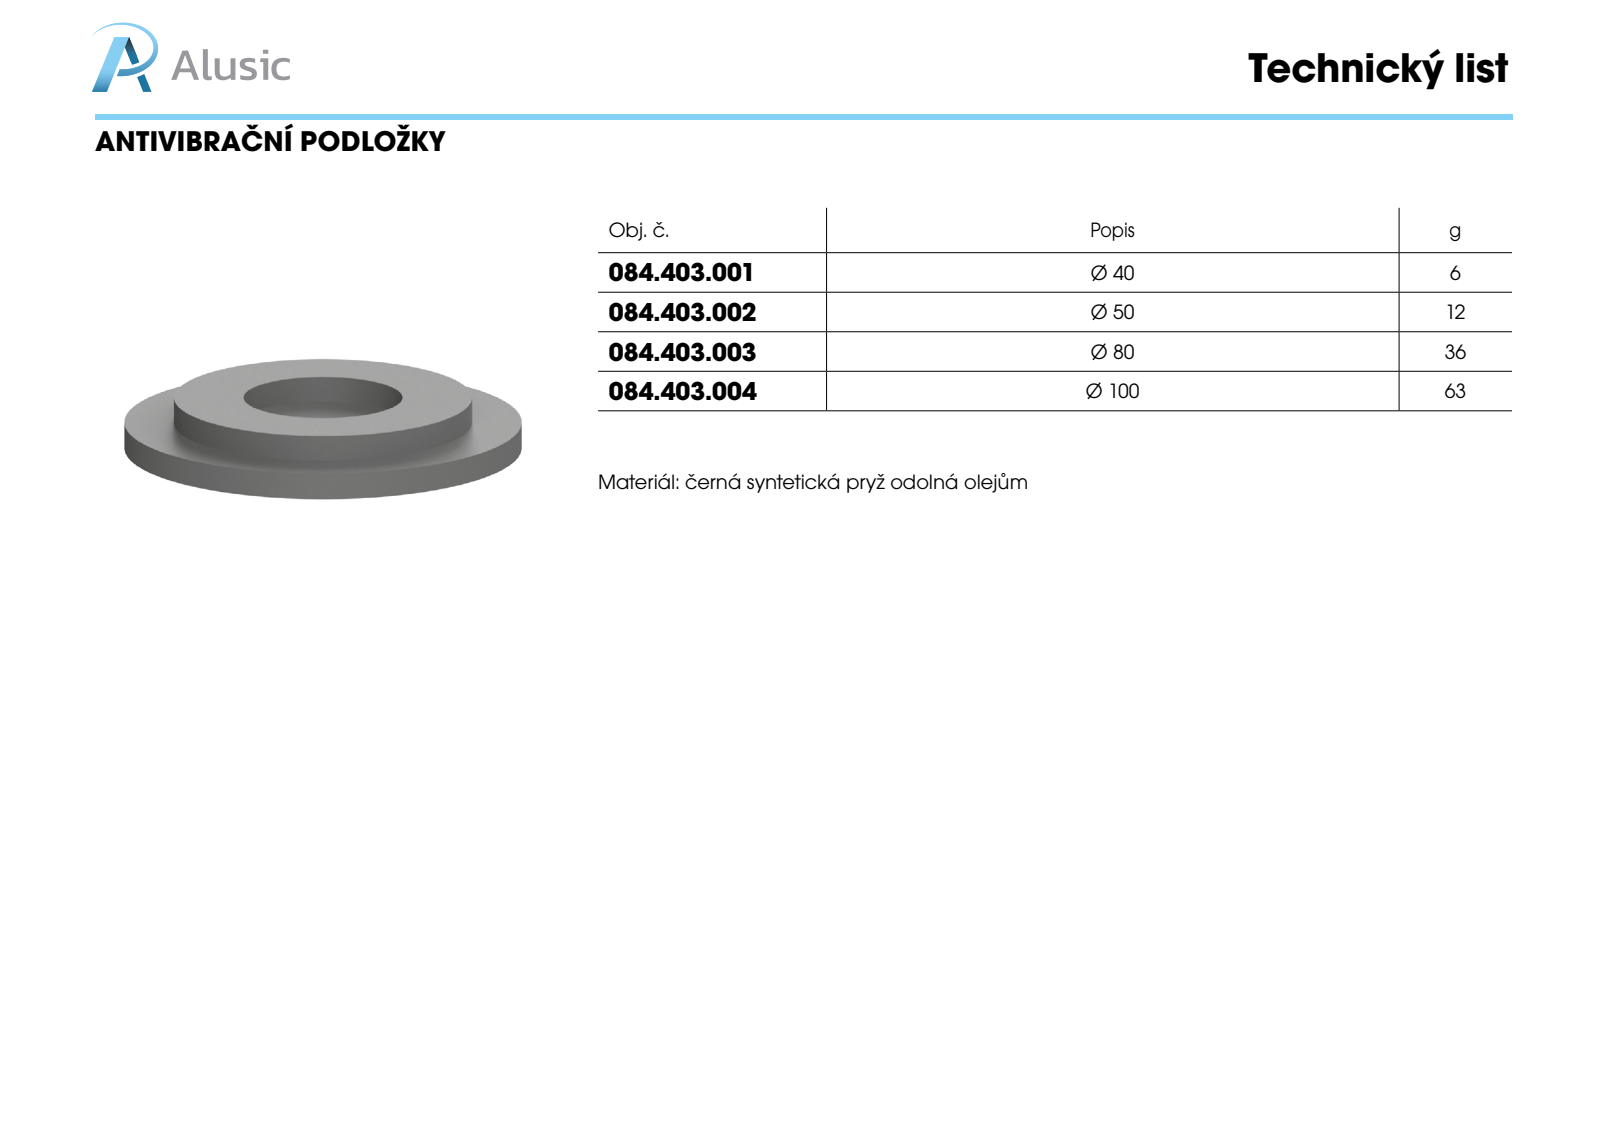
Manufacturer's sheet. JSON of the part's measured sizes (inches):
{"part_name": "084.403.003", "step_written_by": "SolidWorks 2011 (AUTOMOTIVE_DESIGN)", "units": "inches", "bodies": {"solids": 1, "faces": 33, "planar": 12, "cylindrical": 17, "other": 4}, "overall_size": [3.15, 3.15, 0.488], "volume_in3": 1.544, "surface_area_in2": 19.05, "round_holes": [[0.118, 2], [1.024, 1]], "round_bosses_or_shafts": [[0.315, 2], [3.15, 1], [2.717, 1]], "partial_cylinders_radius": [[0.295, 2]], "face_to_face_distances": [0.244, 0.13, 0.114, 0.488, 0.358, 0.591], "hole_center_spacings": [0.886, 1.772]}
